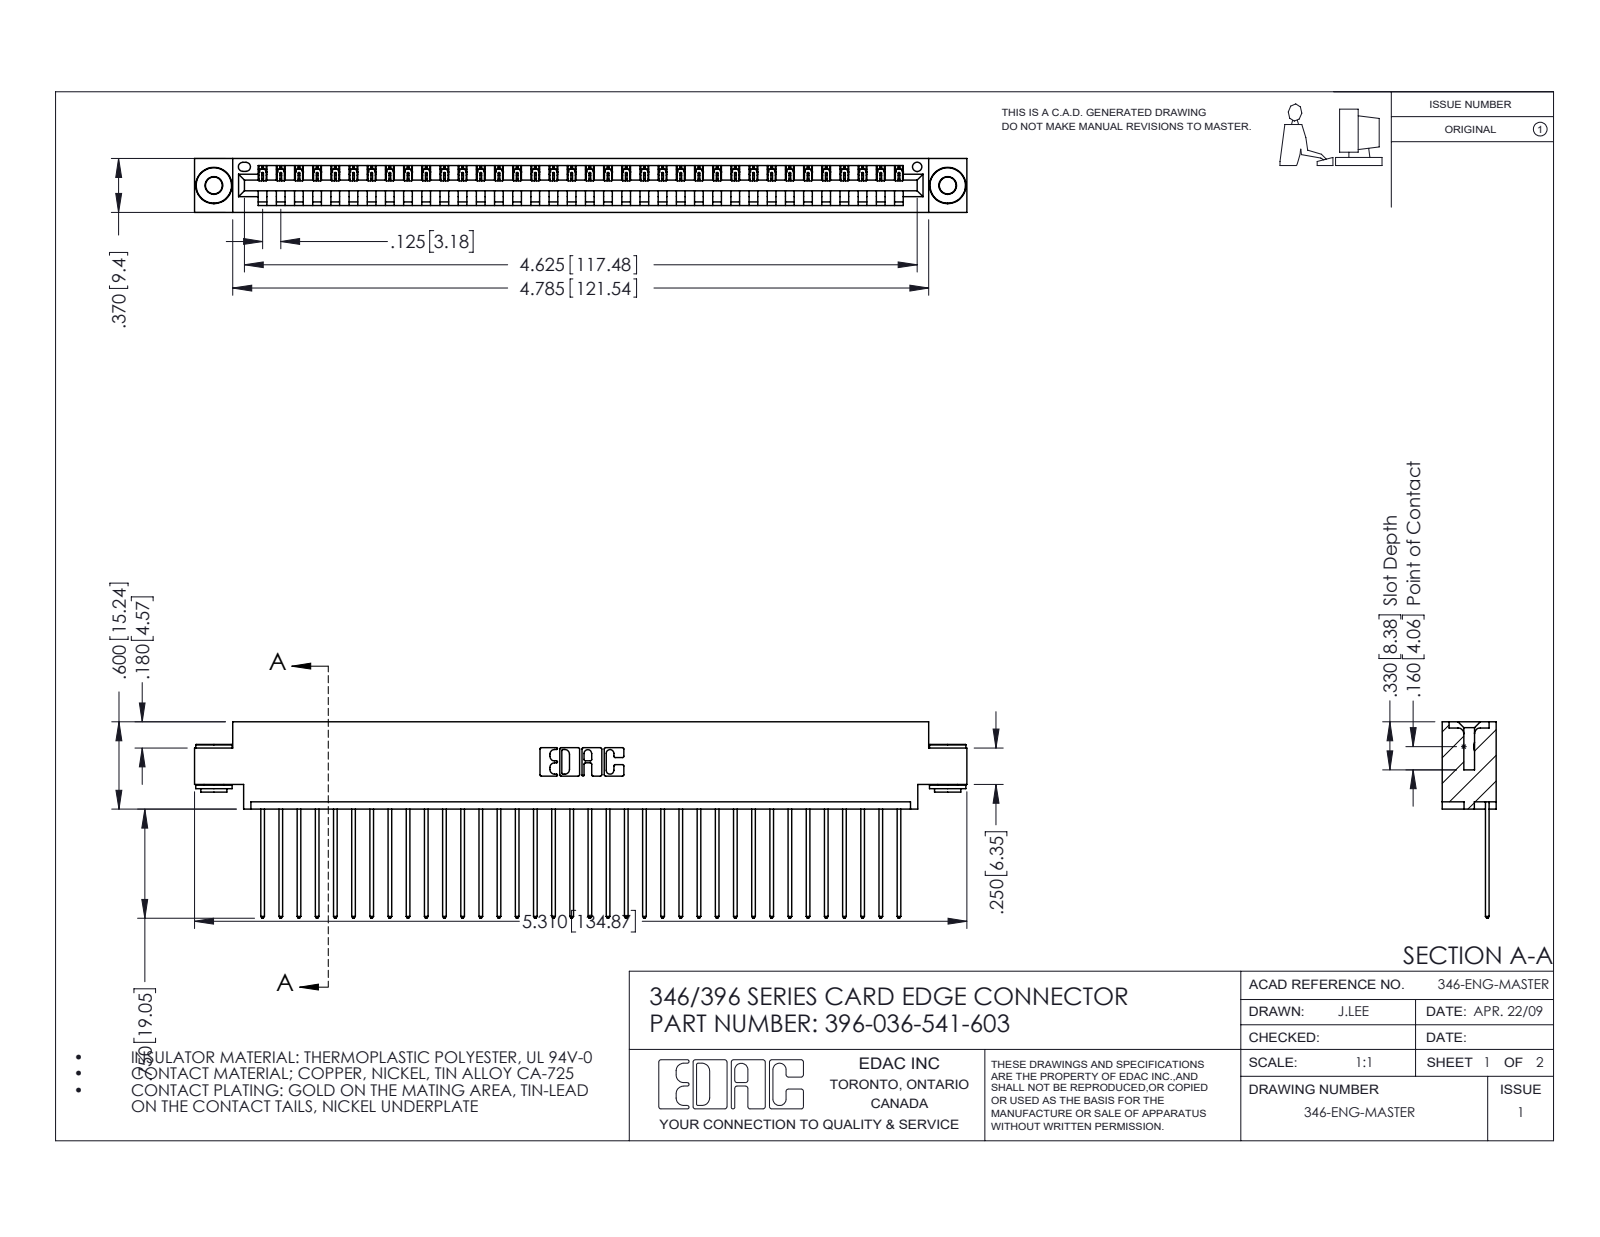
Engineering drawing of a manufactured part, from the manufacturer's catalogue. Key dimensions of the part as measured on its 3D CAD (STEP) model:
Part name (STEP PRODUCT): 345-250-002_345-250-002-102; 396-036-541-603; 346 Part_0.170 Offset - 0.156 Dia-TH; 345-292-001_345-293-141
STEP written by: SolidWorks 2016 (CONFIG_CONTROL_DESIGN)
Units: inches
Bodies: 39 solids, 2252 faces (1530 planar, 714 cylindrical, 8 other)
Overall size (bounding box): 5.31 × 1.35 × 0.37
Volume: 0.784 in³ · Surface area: 26.49 in²
Round holes (diameter × count): ⌀0.116 ×2, ⌀0.156 ×2, ⌀0.064 ×1
Round bosses / shafts (diameter × count): ⌀0.25 ×2, ⌀0.18 ×2, ⌀0.136 ×2
Partial cylindrical surfaces — rounded edges, fillets, slot ends (radius × count): R0.006 ×72, R0.01 ×72, R0.01 ×22, R0.007 ×6, R0.031 ×6, R0.026 ×3, R0.031 ×2, R0.04 ×2
Main face-to-face distances: 0.048, 0.322, 0.37, 0.25, 0.025, 0.072, 0.298, 0.148, 0.222, 0.1
Hole centre spacings: 0.246, 4.836, 5.045
